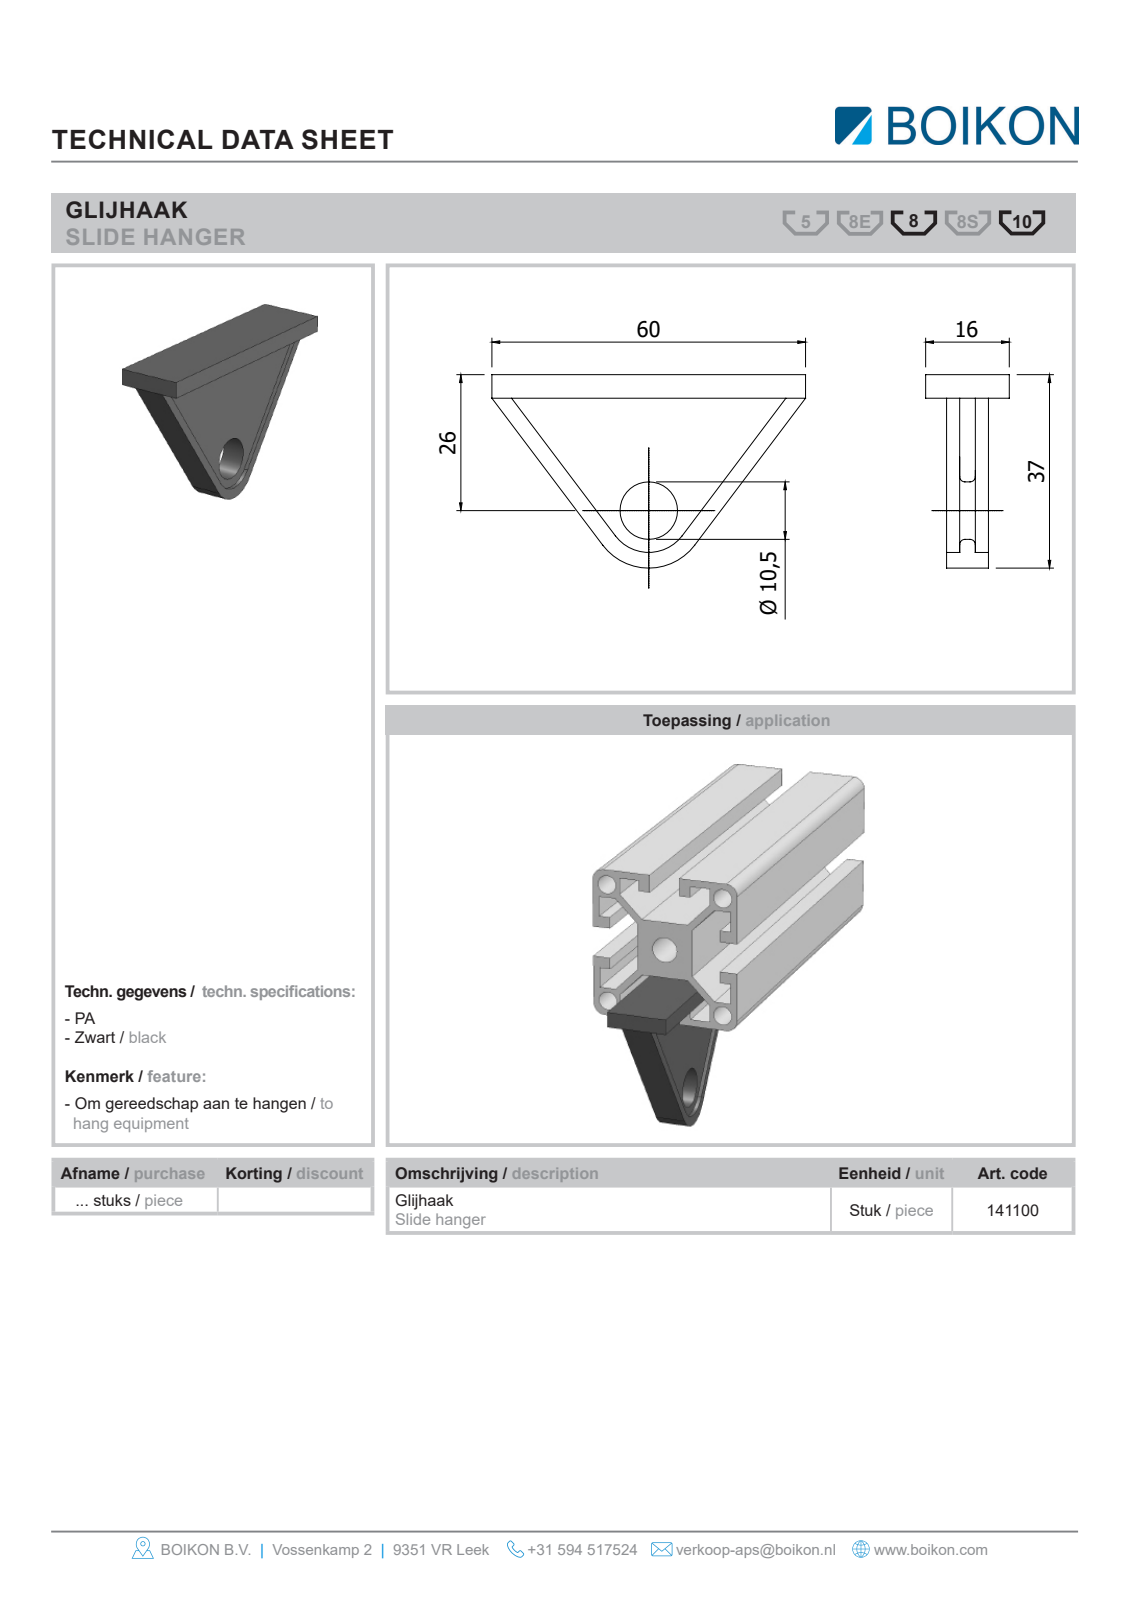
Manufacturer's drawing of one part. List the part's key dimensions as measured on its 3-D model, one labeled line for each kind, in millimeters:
Part name (STEP PRODUCT): Root; 141100 - Glijhaak BOIKON
STEP written by: HiCAD 2013 1802.4 Build 509 (AUTOMOTIVE_DESIGN)
Units: millimetres
Bodies: 1 solid, 21 faces (17 planar, 4 cylindrical, 0 other)
Overall size (bounding box): 60 × 40.24 × 16
Volume: 11 090 mm³ · Surface area: 5 591 mm²
Round holes (diameter × count): ⌀10.5 ×1
Partial cylindrical surfaces — rounded edges, fillets, slot ends (radius × count): R7 ×1, R8 ×1
Main face-to-face distances: 4, 6, 5, 11, 12, 1, 7, 16, 8, 2
